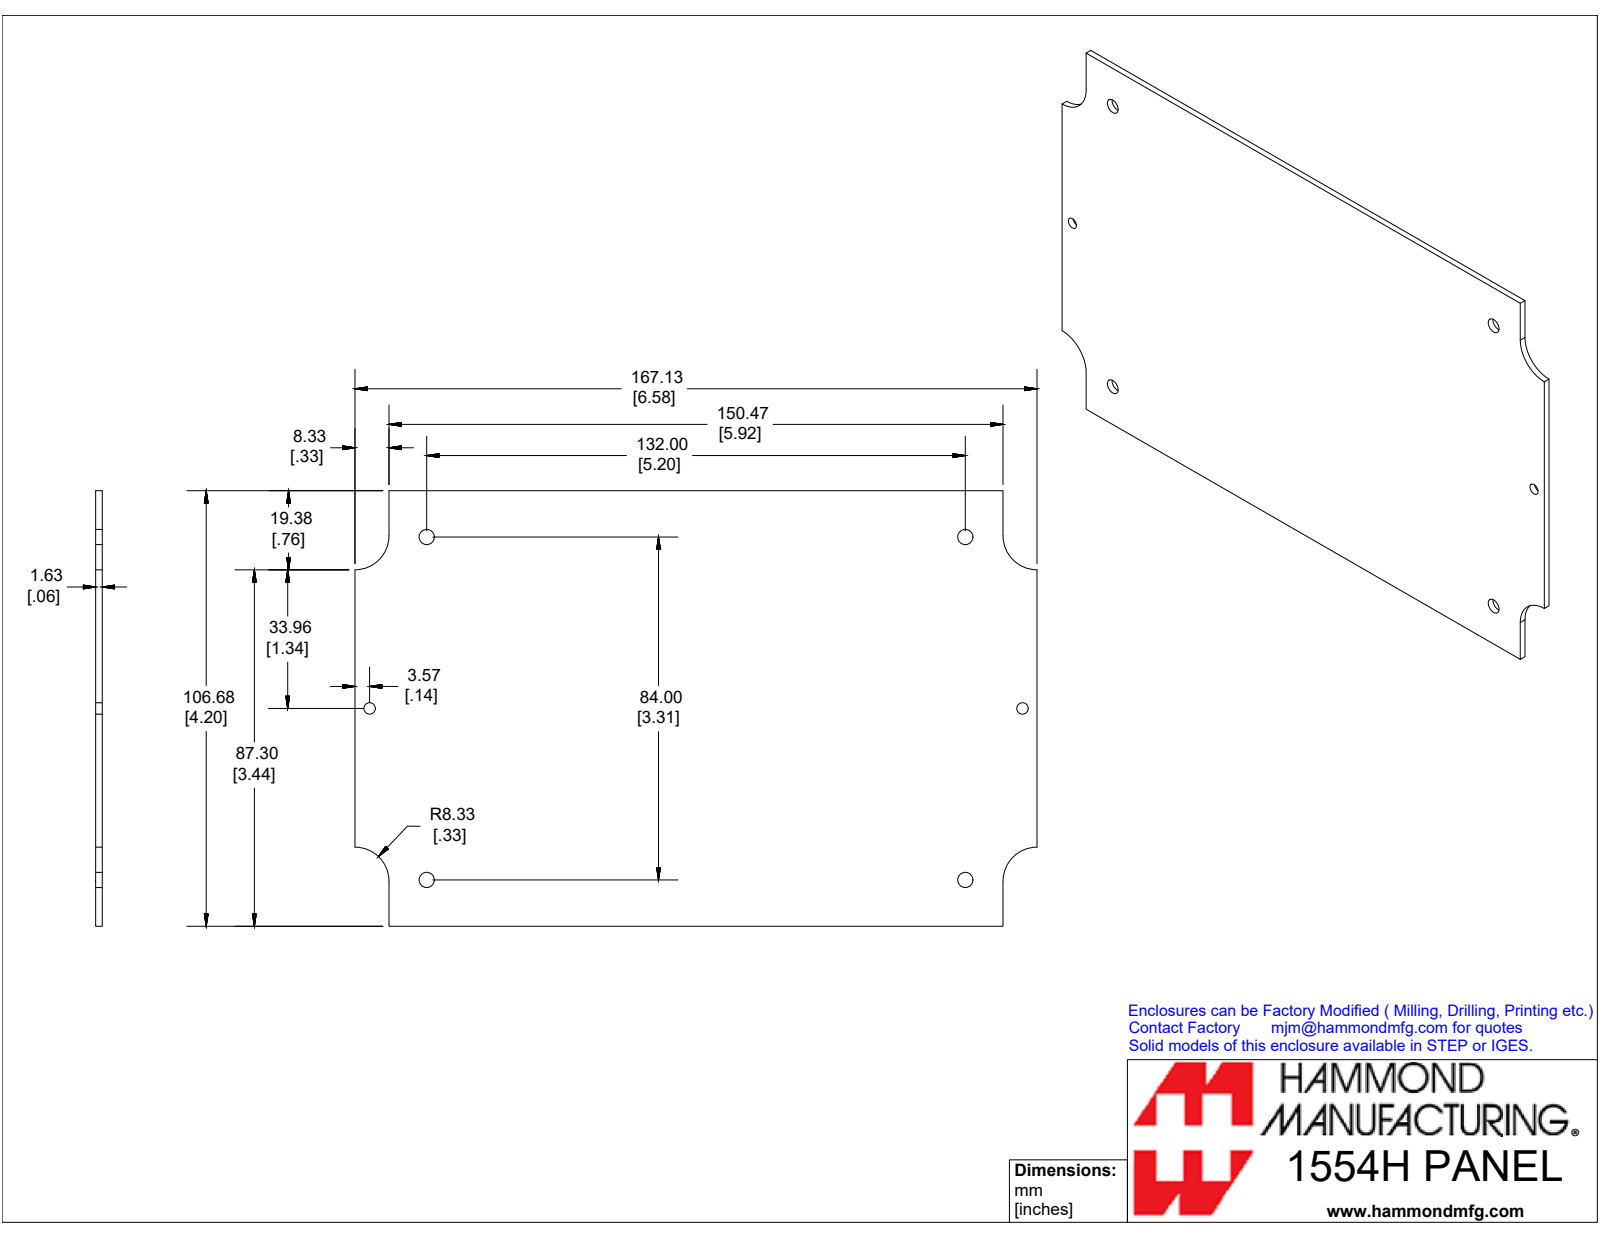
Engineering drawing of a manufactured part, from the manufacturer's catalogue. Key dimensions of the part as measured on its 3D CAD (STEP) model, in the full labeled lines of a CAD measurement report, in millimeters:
Part name (STEP PRODUCT): 1554HPL
STEP written by: SolidWorks 2019 (CONFIG_CONTROL_DESIGN)
Units: millimetres
Bodies: 1 solid, 20 faces (10 planar, 10 cylindrical, 0 other)
Overall size (bounding box): 167.1 × 106.7 × 1.6
Volume: 27 940 mm³ · Surface area: 35 350 mm²
Round holes (diameter × count): ⌀3.7 ×4, ⌀2.8 ×2
Partial cylindrical surfaces — rounded edges, fillets, slot ends (radius × count): R8.3 ×4
Main face-to-face distances: 1.6, 106.7, 167.1, 8.3, 158.8, 150.5
Hole centre spacings: 44.4, 152, 84.3, 132, 156.6, 160
